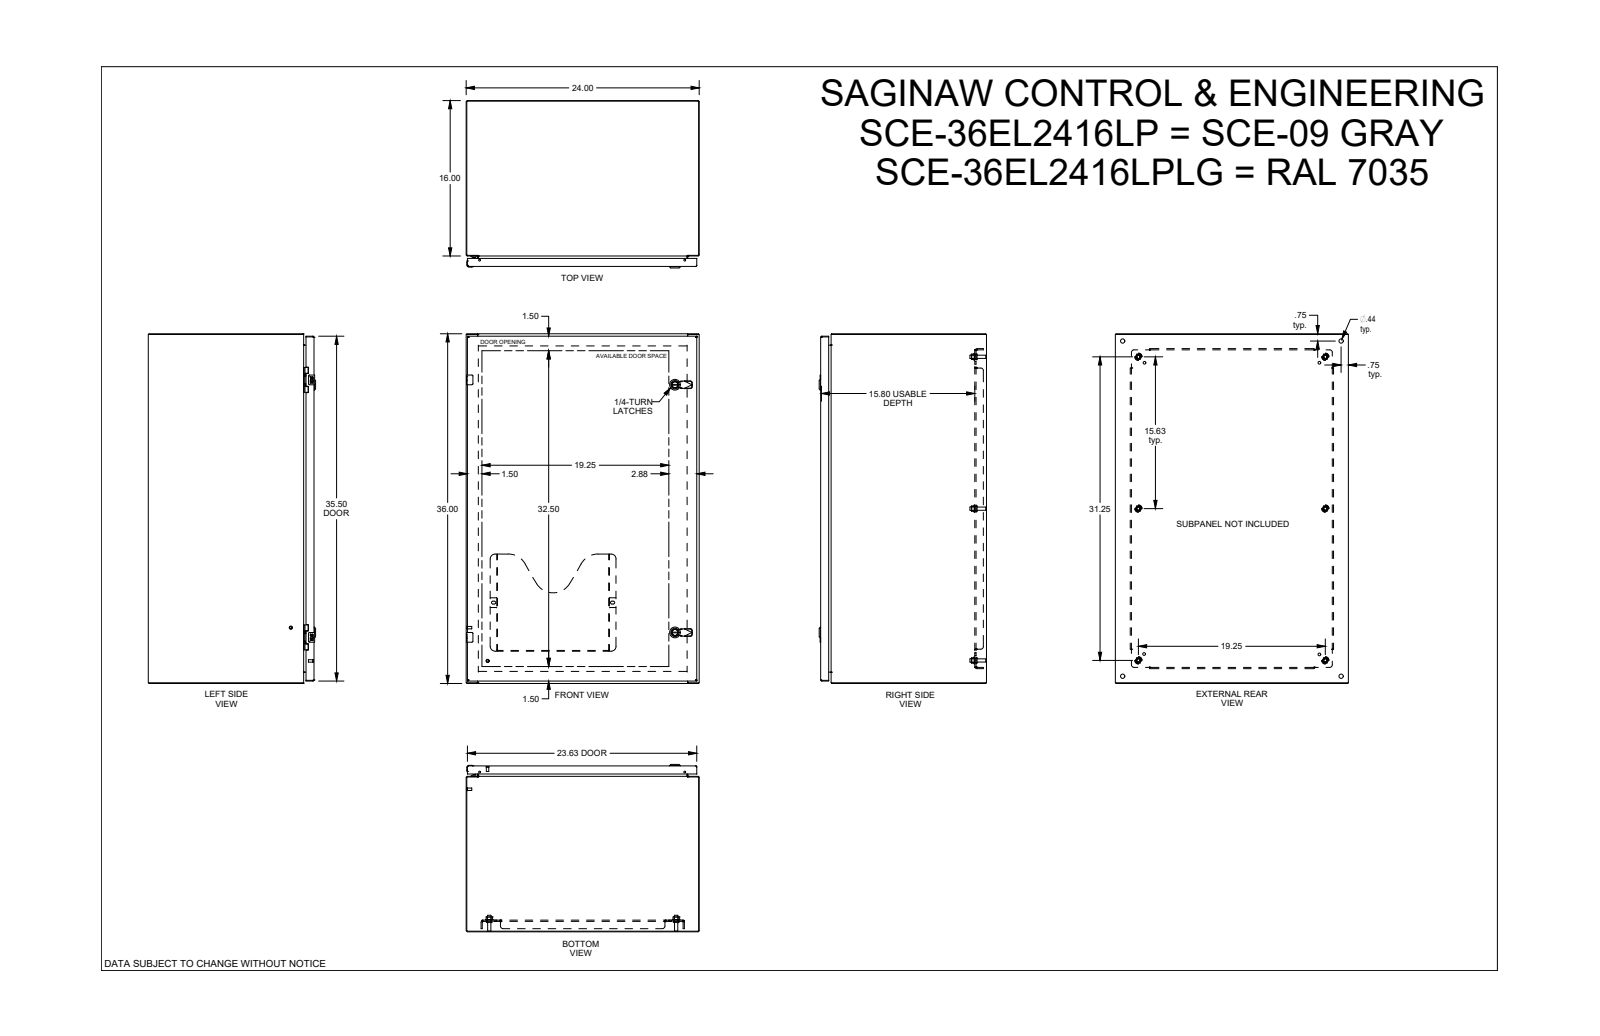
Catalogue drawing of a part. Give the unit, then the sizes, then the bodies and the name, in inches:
Units: inches
Overall size (bounding box): 36 × 24 × 17.23
Round holes (diameter × count): ⌀0.367 ×6, ⌀0.5 ×6, ⌀0.172 ×4, ⌀0.205 ×4, ⌀0.244 ×4, ⌀0.266 ×4, ⌀0.281 ×4, ⌀0.375 ×4, ⌀0.437 ×4, ⌀0.04 ×2, ⌀0.188 ×2, ⌀0.197 ×2
Round bosses / shafts (diameter × count): ⌀0.366 ×6, ⌀0.332 ×6, ⌀0.17 ×6, ⌀0.25 ×4, ⌀0.248 ×4, ⌀0.24 ×4, ⌀0.196 ×3, ⌀1.102 ×2
Partial cylindrical surfaces — rounded edges, fillets, slot ends (radius × count): R0.012 ×56, R0.01 ×40, R0.015 ×24, R0.02 ×20, R0.04 ×17, R0.06 ×13, R0.029 ×12, R0.1 ×12
Main face-to-face distances: 0.075, 23.925, 0.075, 0.06, 17.073, 16.998, 17.013, 16.938, 1.2, 15.873
Hole centre spacings: 0.985, 26.5, 0.02, 0.493, 0.494, 2.298, 4.493, 15.625
Volume: 406.4 in³ · Surface area: 9 927 in²
Bodies: 51 solids, 2989 faces (1139 planar, 888 cylindrical, 962 other)
Part name (STEP PRODUCT): SCE-36EL2416LP
STEP written by: SolidWorks 2021 (AUTOMOTIVE_DESIGN)
